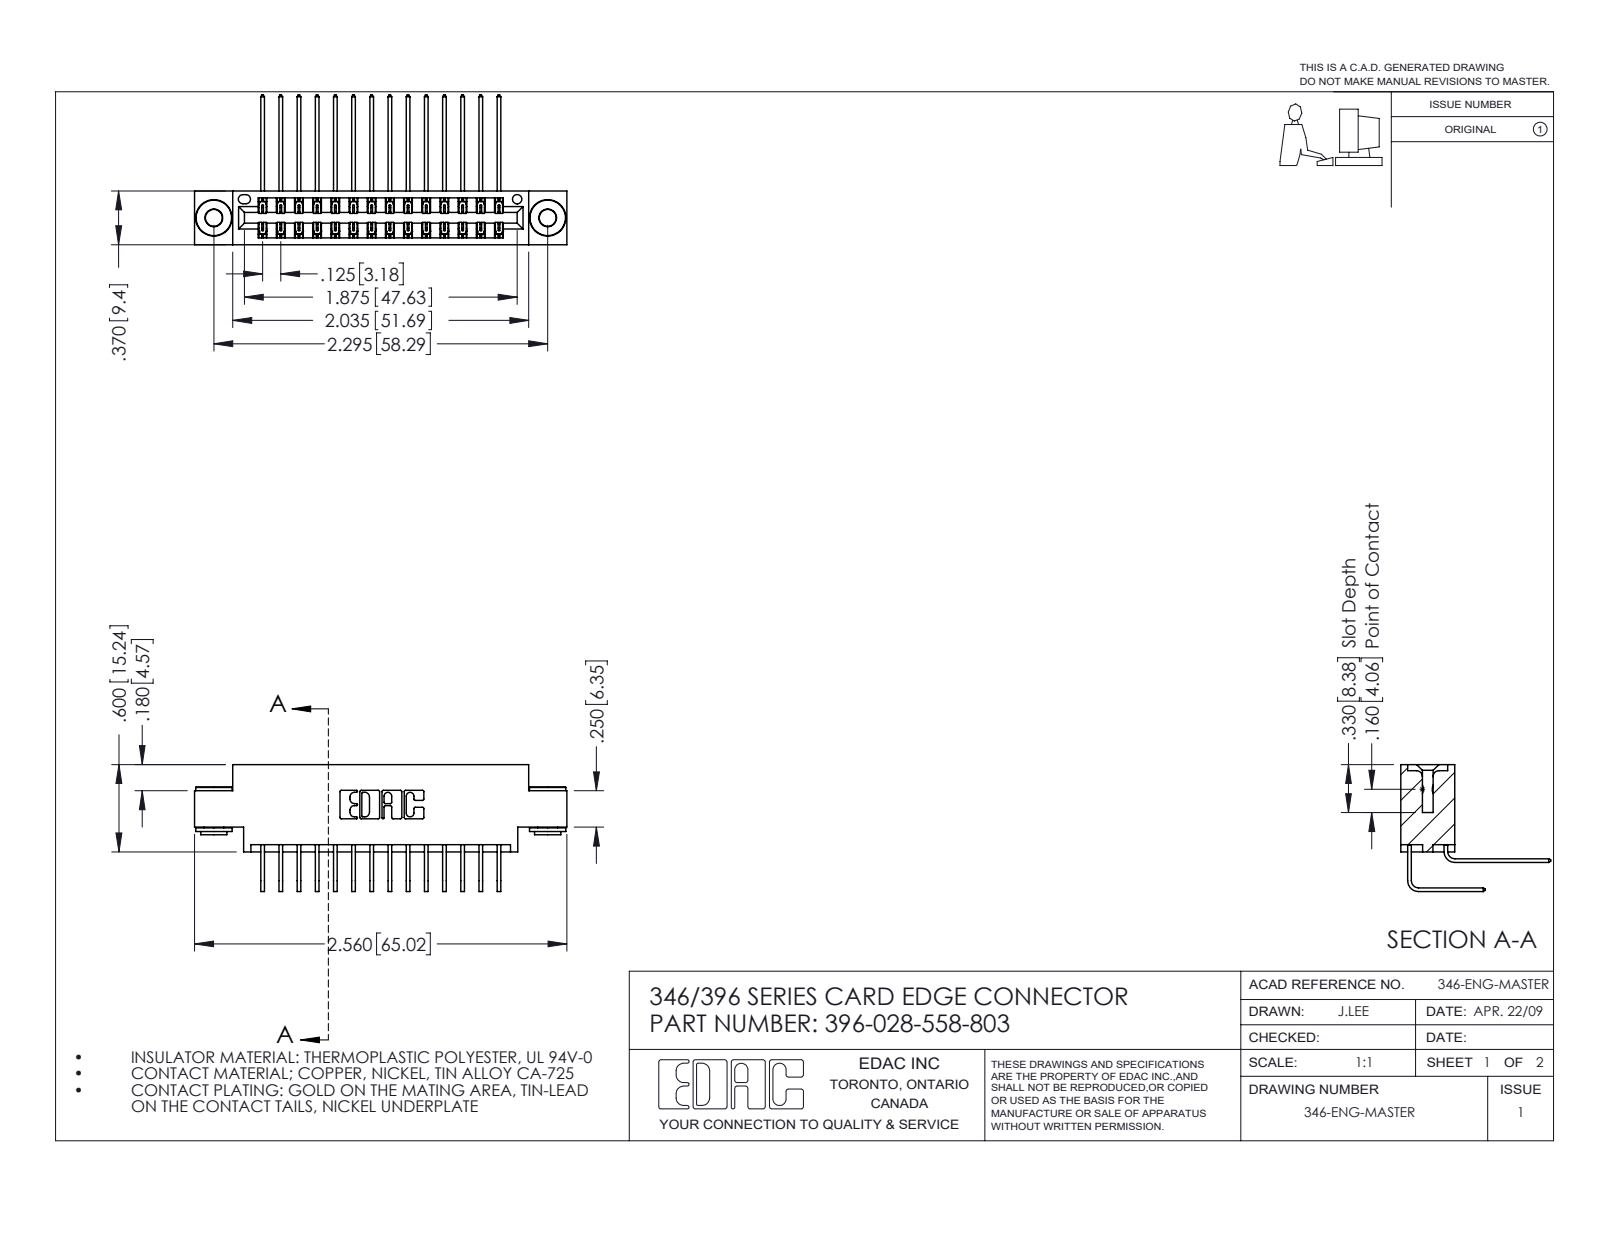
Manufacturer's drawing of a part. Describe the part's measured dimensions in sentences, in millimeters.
The part is named "345-292-001_558 Tail - 2; 396-028-558-803; 345-250-002_345-250-002-102; 346 Part_0.170 Offset - 0.156 Dia-TH (+1 more)". Its 3-D file was written by "SolidWorks 2016 (CONFIG_CONTROL_DESIGN)". It is 31 solids with 1676 faces: 1126 planar, 542 cylindrical and 8 other. Overall it measures 65 by 26.2 by 22.2 millimeters. Its volume is 6 150 cubic millimeters and its surface area 9 181 square millimeters. Round holes: 2 of diameter 2.9, 2 of diameter 4, 1 of diameter 1.6. Round bosses or shafts: 2 of diameter 6.4, 2 of diameter 4.6, 2 of diameter 3.5. Partial cylindrical surfaces (rounded edges, fillets, slot ends): 42 of radius 0.2, 22 of radius 0.3, 6 of radius 0.2, 6 of radius 0.8, 3 of radius 0.7, 2 of radius 0.4, 2 of radius 0.6, 2 of radius 0.6. The main face-to-face distances are 1.2, 8.2, 9.4, 6.4, 0.6, 1.8, 7.6, 7, 3.8, 5.6. The hole center spacings are 6.2, 53.1, 58.3.
